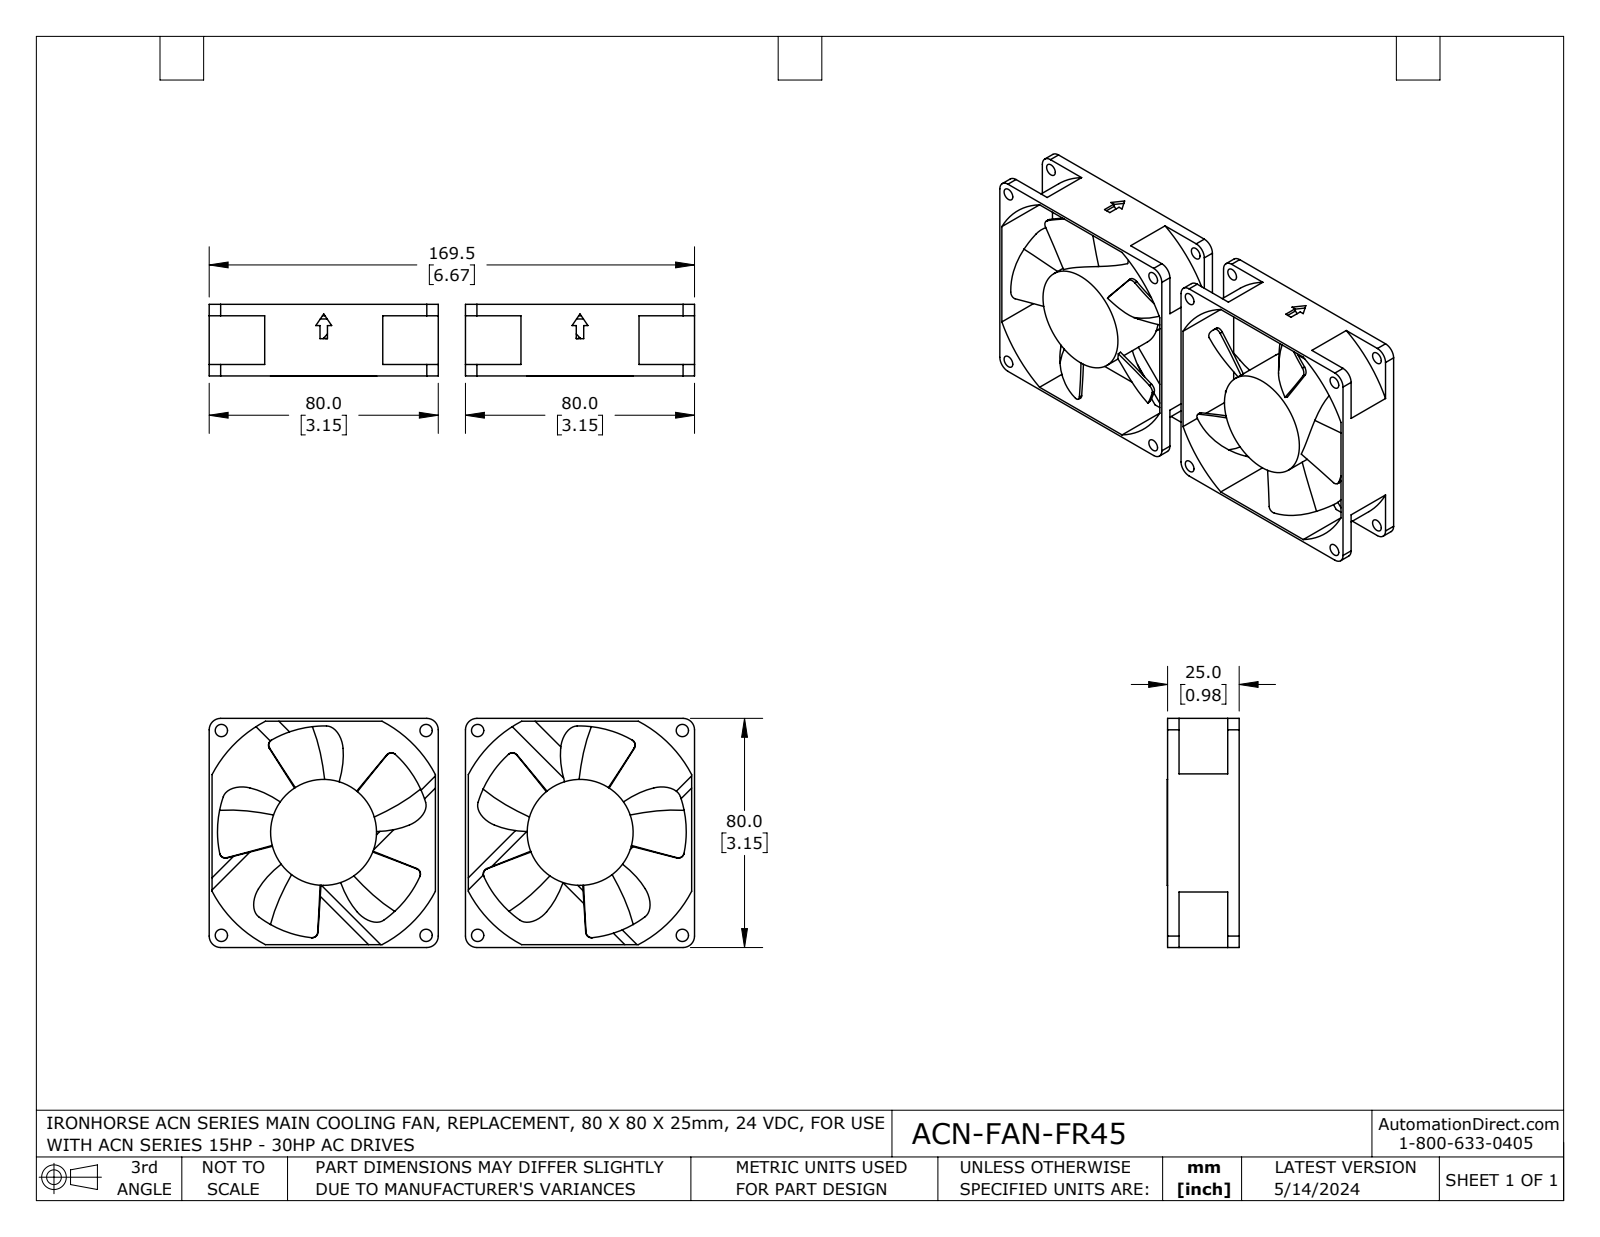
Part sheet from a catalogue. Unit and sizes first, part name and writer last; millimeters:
Units: millimetres
Overall size (bounding box): 169.5 × 80 × 25.1
Round holes (diameter × count): ⌀4.3 ×8, ⌀29.5 ×2
Round bosses / shafts (diameter × count): ⌀37 ×2, ⌀33 ×2
Partial cylindrical surfaces — rounded edges, fillets, slot ends (radius × count): R2 ×10, R4 ×8, R44 ×2, R45 ×2
Main face-to-face distances: 1, 79, 80, 89.5, 78, 4, 21, 25, 5.1, 25.1
Hole centre spacings: 50.6, 71.5, 89.5, 64.5, 101.1, 114.6, 130.3, 18
Volume: 117 000 mm³ · Surface area: 66 190 mm²
Bodies: 4 solids, 260 faces (82 planar, 88 cylindrical, 90 other)
Part name (STEP PRODUCT): ACN-FAN-FR45
STEP written by: SolidWorks 2021 (AUTOMOTIVE_DESIGN)
